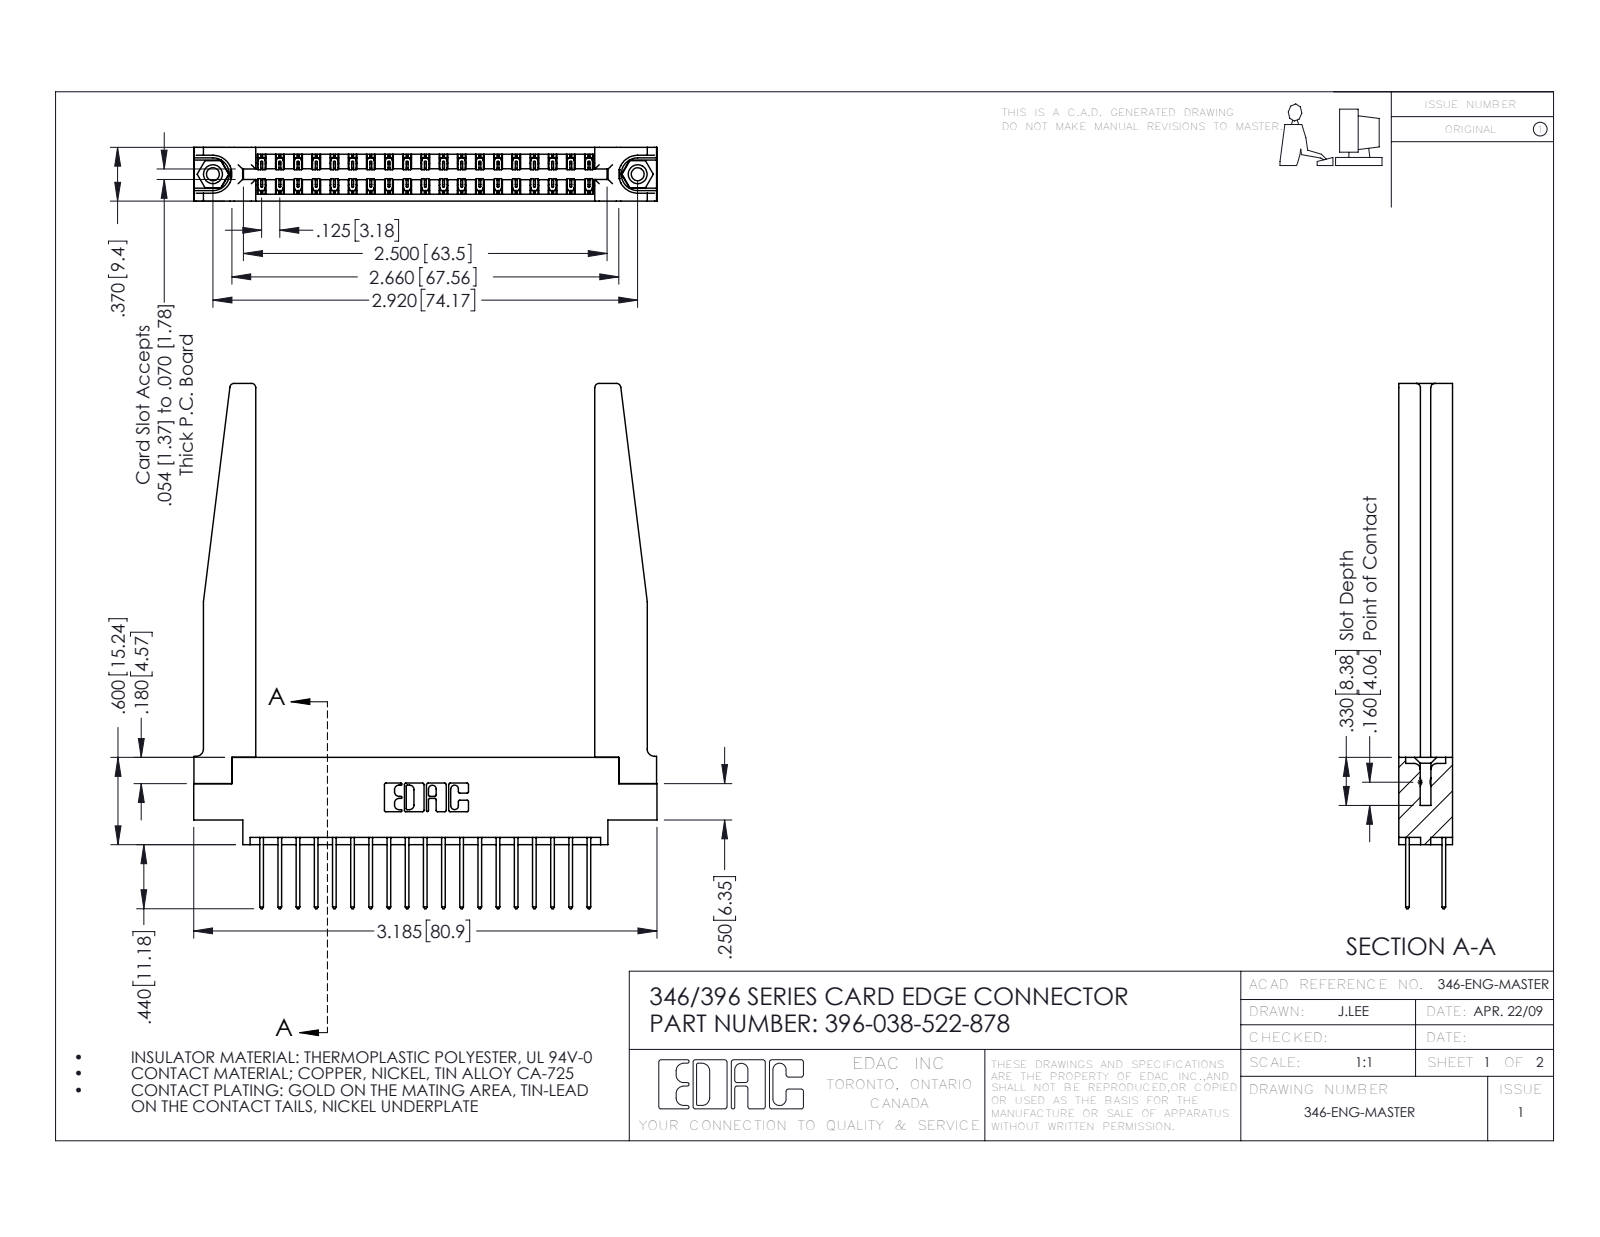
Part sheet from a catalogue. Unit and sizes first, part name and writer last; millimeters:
Units: millimetres
Overall size (bounding box): 91.7 × 80.9 × 9.4
Round holes (diameter × count): ⌀2.3 ×2, ⌀3.2 ×2, ⌀4 ×2, ⌀1.6 ×1
Round bosses / shafts (diameter × count): ⌀3.9 ×2
Partial cylindrical surfaces — rounded edges, fillets, slot ends (radius × count): R0.2 ×57, R0.3 ×38, R0.3 ×22, R0.8 ×8, R0.2 ×6, R0.8 ×6, R0.7 ×3, R0.4 ×2
Main face-to-face distances: 9.4, 1.2, 8.2, 1.8, 3.8, 3.8, 6.4, 7.6, 0.6, 7
Hole centre spacings: 6.2, 68.9, 74.2
Volume: 14 600 mm³ · Surface area: 17 330 mm²
Bodies: 43 solids, 2336 faces (1552 planar, 732 cylindrical, 52 other)
Part name (STEP PRODUCT): 346 Part_0.170 Offset - 0.156 Dia-TH; 346-220-078_345-220-078; 345-250-001_345-250-001-102; 345-292-001_345-293-122 (+1 more)
STEP written by: SolidWorks 2016 (CONFIG_CONTROL_DESIGN)
